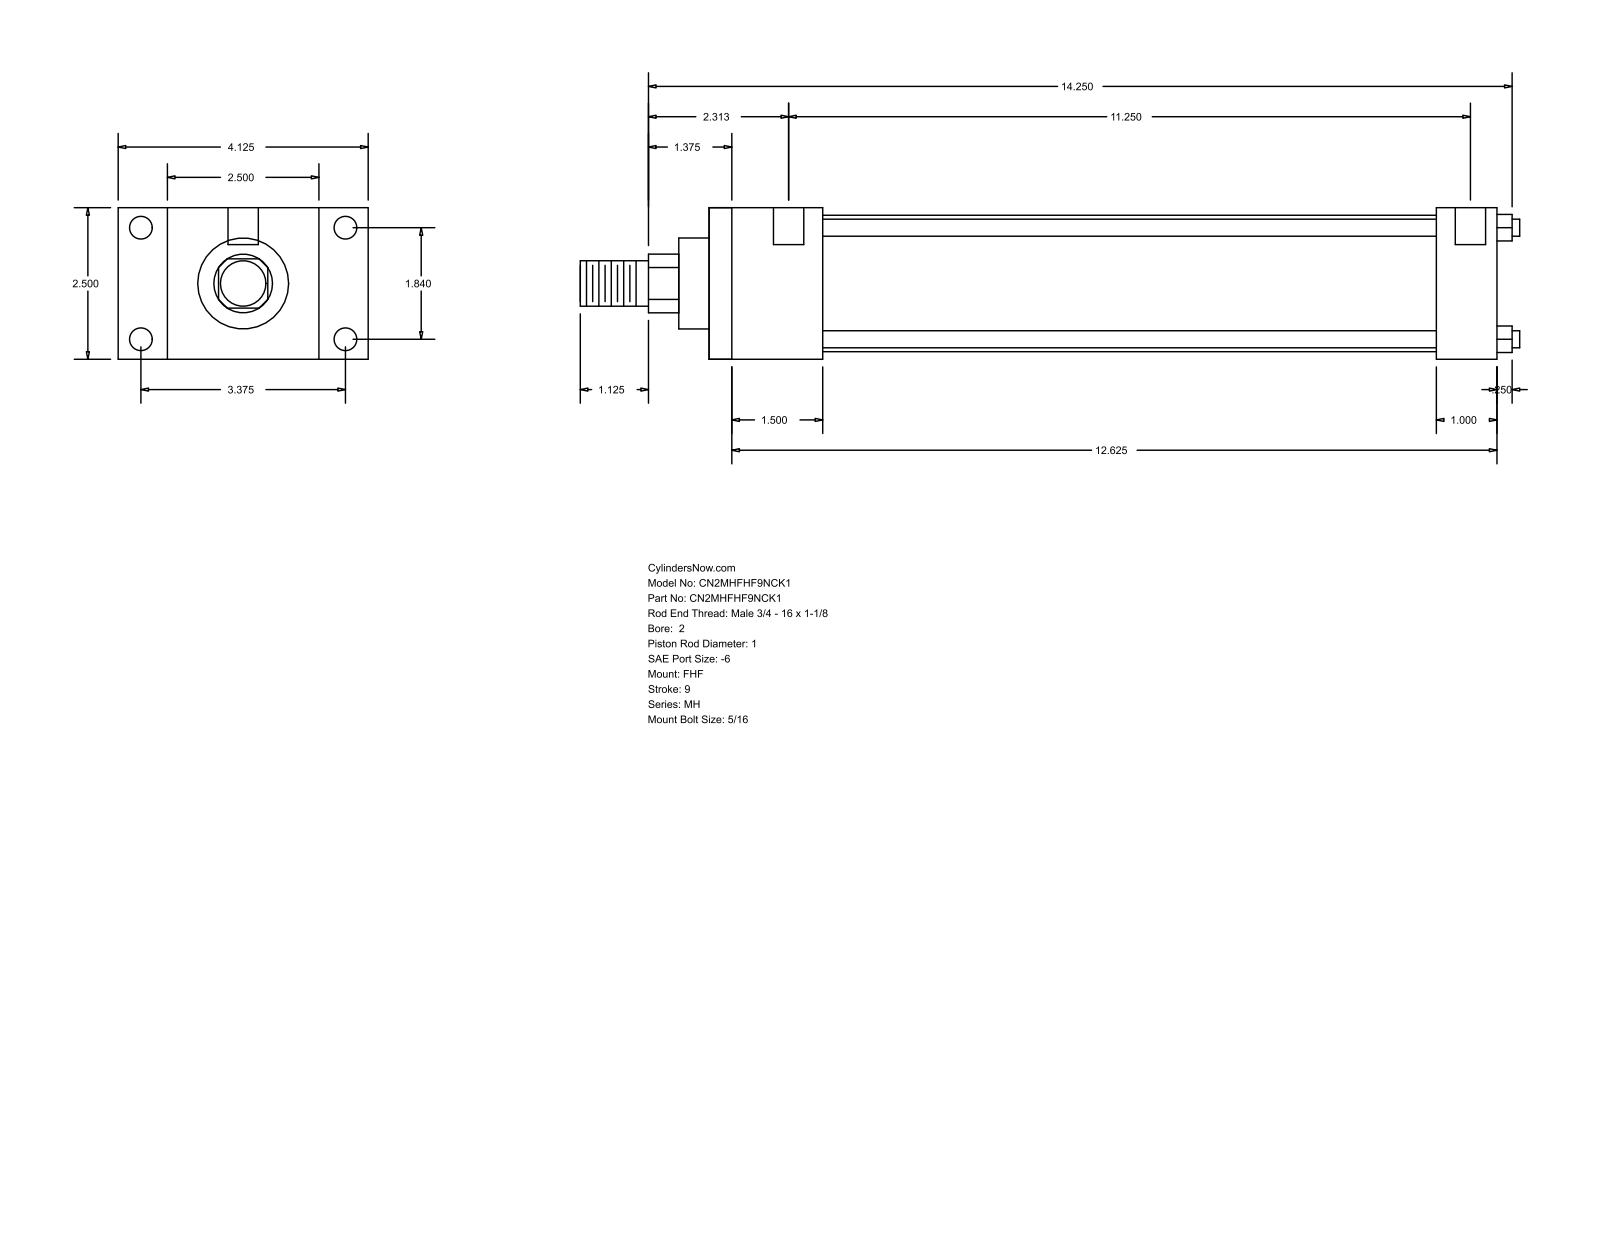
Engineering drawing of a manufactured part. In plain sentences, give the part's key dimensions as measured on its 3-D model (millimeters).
The part is named "MH_FHF__0200_1". Its 3-D file was written by "GSSL Pune (CONFIG_CONTROL_DESIGN)". It is 0 solids with 88 faces: 60 planar, 28 cylindrical and 0 other. Overall it measures 393.7 by 104.78 by 63.5 millimeters. Round holes: 4 of diameter 5.56, 4 of diameter 9.53, 2 of diameter 12.7. Round bosses or shafts: 4 of diameter 7.14, 1 of diameter 57.15, 1 of diameter 38.1, 1 of diameter 25.4, 1 of diameter 19.05. Partial cylindrical surfaces (rounded edges, fillets, slot ends): 1 of radius 12.29. The main face-to-face distances are 63.5, 330.2, 47.63, 282.57, 20.64, 84.14, 104.78, 25.4, 304.8, 257.17. The hole center spacings are 46.74, 85.72, 97.63, 293.68, 3.17, 4.76, 285.75, 288.92.
